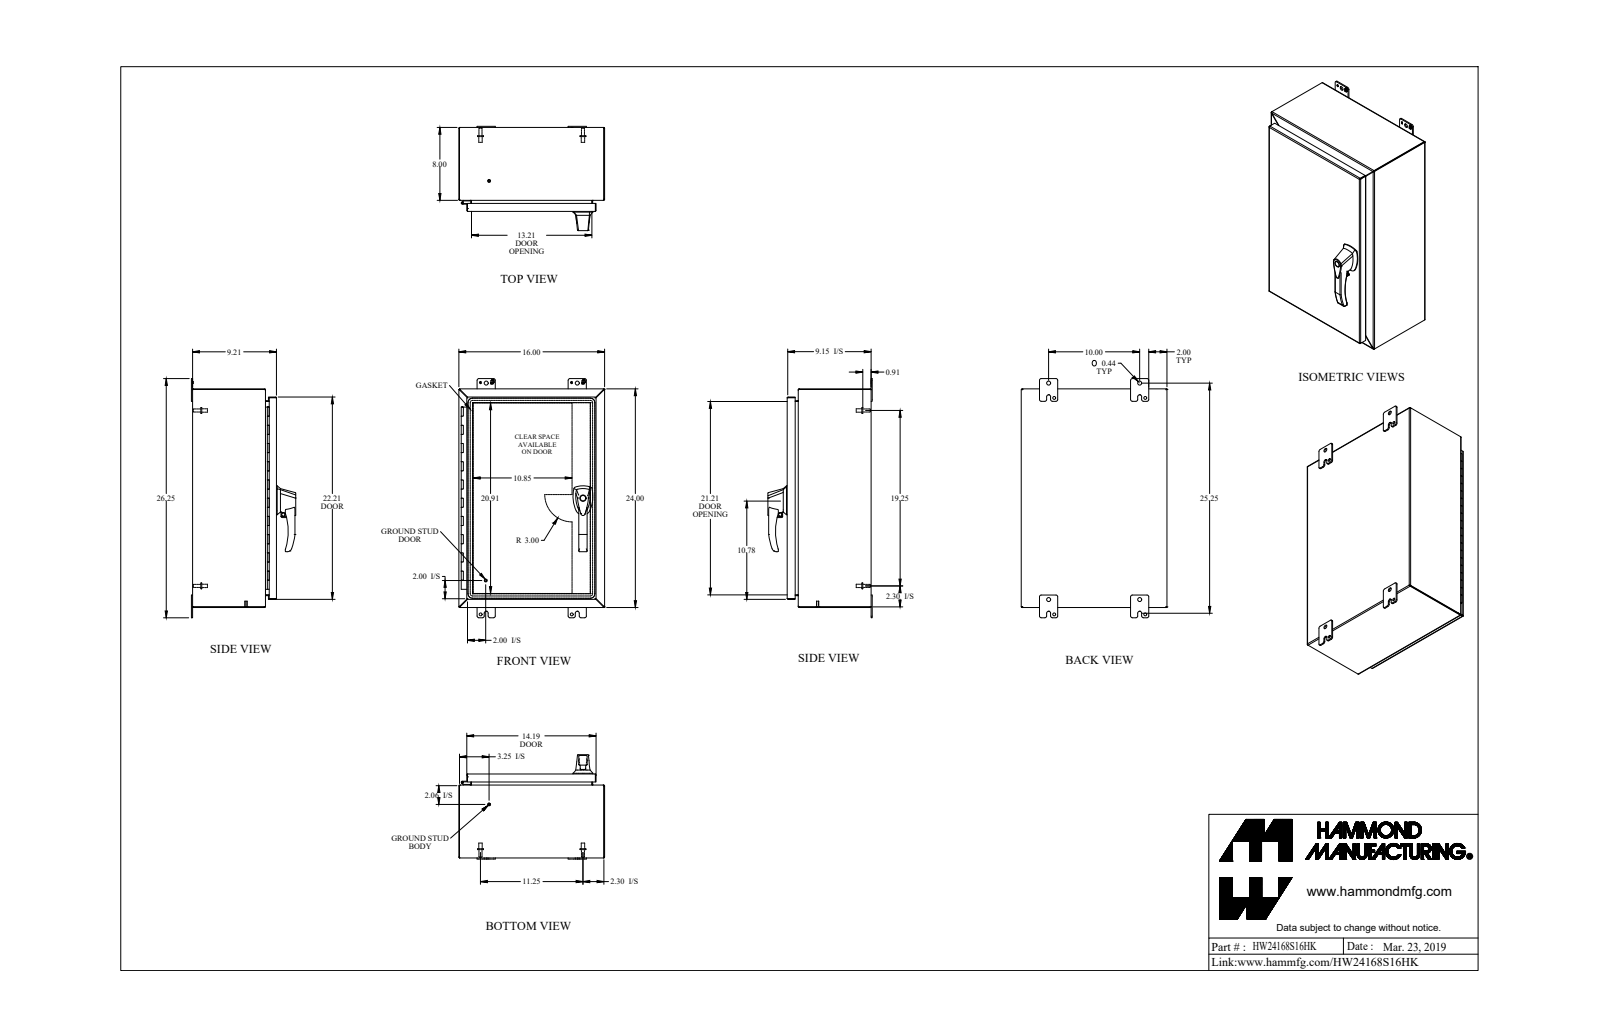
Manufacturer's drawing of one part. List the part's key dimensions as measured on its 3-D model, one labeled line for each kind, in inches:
Part name (STEP PRODUCT): HW24168S16HK
STEP written by: SolidWorks 2018 (AUTOMOTIVE_DESIGN)
Units: inches
Bodies: 46 solids, 1420 faces (688 planar, 580 cylindrical, 152 other)
Overall size (bounding box): 26.25 × 16 × 11.45
Volume: 145.1 in³ · Surface area: 3 657 in²
Round holes (diameter × count): ⌀0.176 ×6, ⌀0.313 ×5, ⌀0.25 ×3, ⌀0.413 ×3, ⌀0.196 ×2, ⌀0.256 ×2, ⌀0.265 ×2, ⌀0.394 ×2, ⌀0.437 ×2, ⌀0.11 ×1, ⌀0.233 ×1, ⌀0.265 ×1
Round bosses / shafts (diameter × count): ⌀0.375 ×9, ⌀0.25 ×7, ⌀0.156 ×6, ⌀0.65 ×4, ⌀0.332 ×4, ⌀0.313 ×4, ⌀1 ×3, ⌀0.51 ×3
Partial cylindrical surfaces — rounded edges, fillets, slot ends (radius × count): R0.25 ×27, R0.188 ×24, R0.036 ×20, R0.108 ×20, R0.06 ×12, R0.125 ×9, R0.045 ×8, R0.218 ×8
Main face-to-face distances: 0.072, 0.072, 15.928, 9.138, 9.066, 9.138, 9.21, 23.928, 15.856, 7.928
Hole centre spacings: 1.111, 8.118, 8.119, 16.237, 1.338, 6.78, 7.576, 7.577
